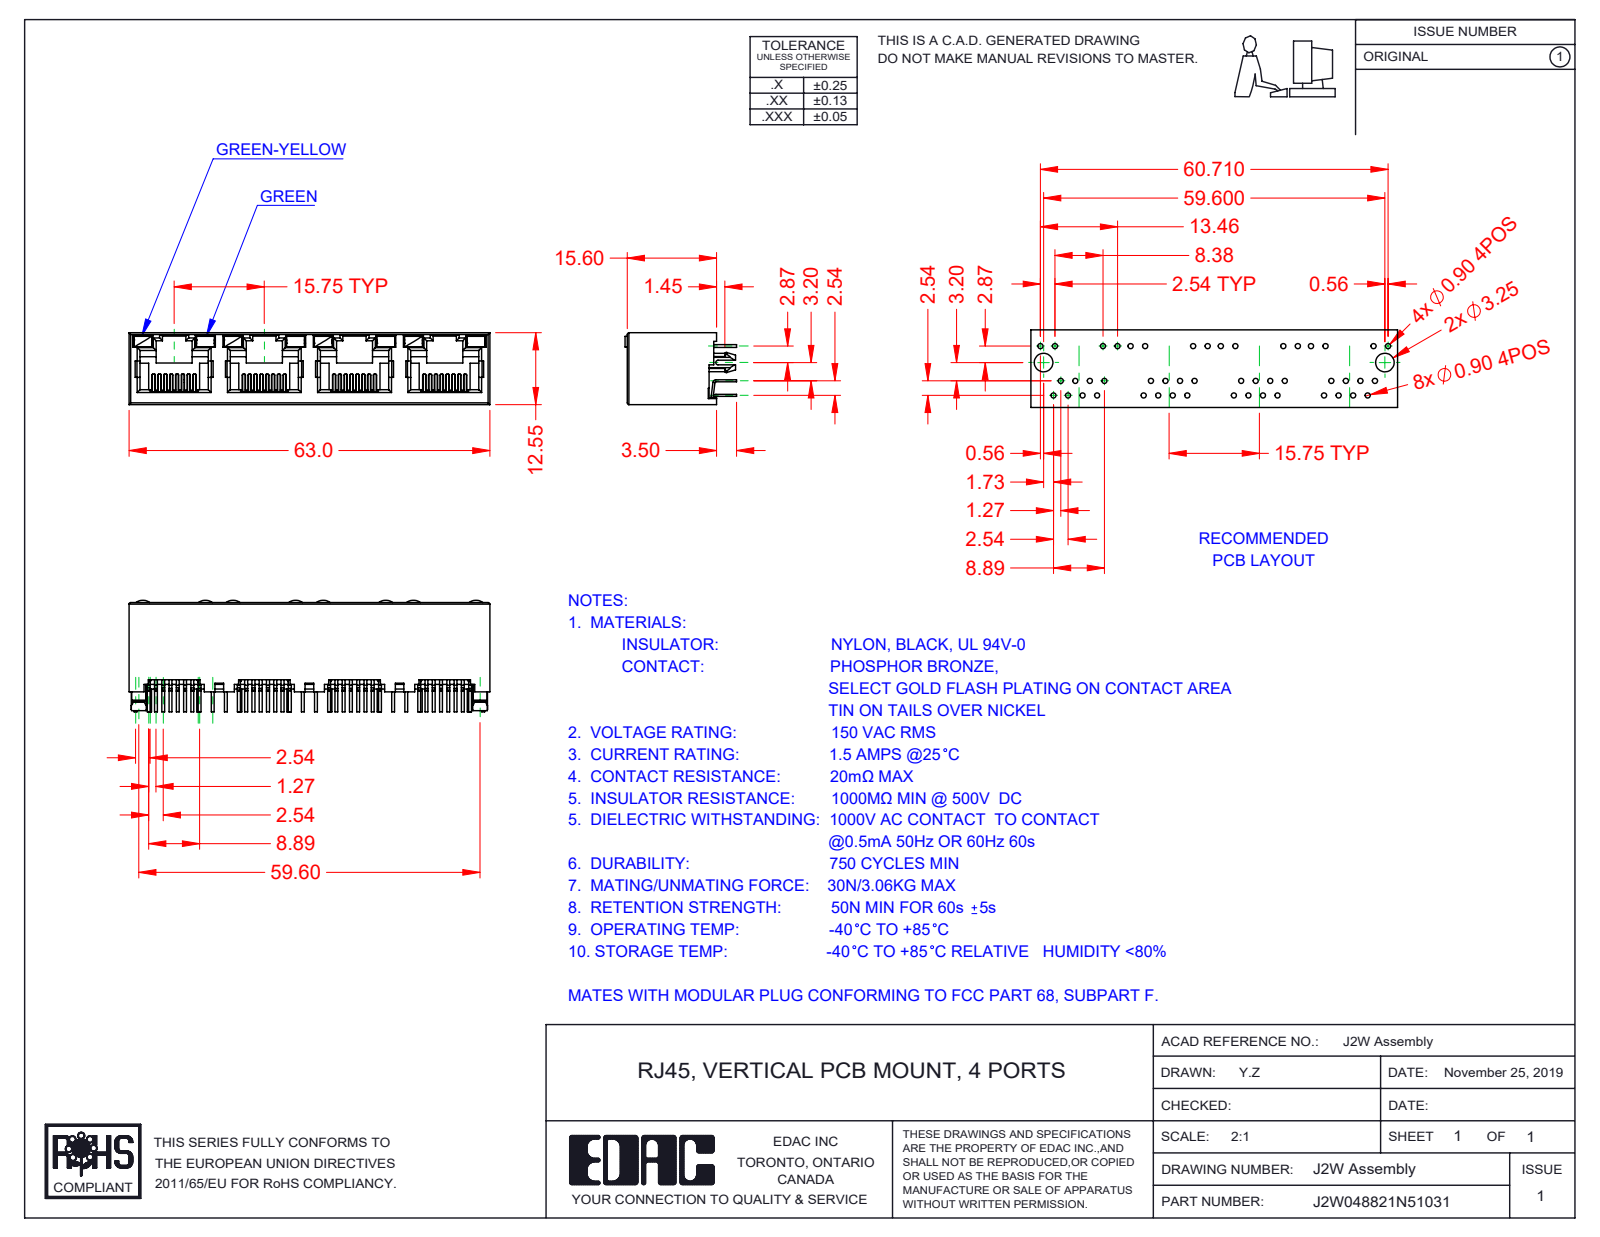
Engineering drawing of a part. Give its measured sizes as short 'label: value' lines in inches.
name: 2W LED LH_5-Green-Yellow; 2W Insulator; J2W048821N53131; 2W LED RH_3-Green (+2 more)
written by: SolidWorks 2016 (CONFIG_CONTROL_DESIGN)
unit: in
bodies: 45 solids, 3139 faces (2600 planar, 481 cylindrical, 58 other)
size: 2.48 × 0.768 × 0.494
volume: 0.326 in³; area: 20.37 in²
rounds: 64× R0.006, 29× R0.008, 28× R0.02, 14× R0.012, 8× R0.018, 8× R0.079, 2× R0.01, 2× R0.059
face distances: 0.494, 0.469, 0.026, 0.62, 0.014, 0.059, 0.031, 0.024, 0.445, 1.24
